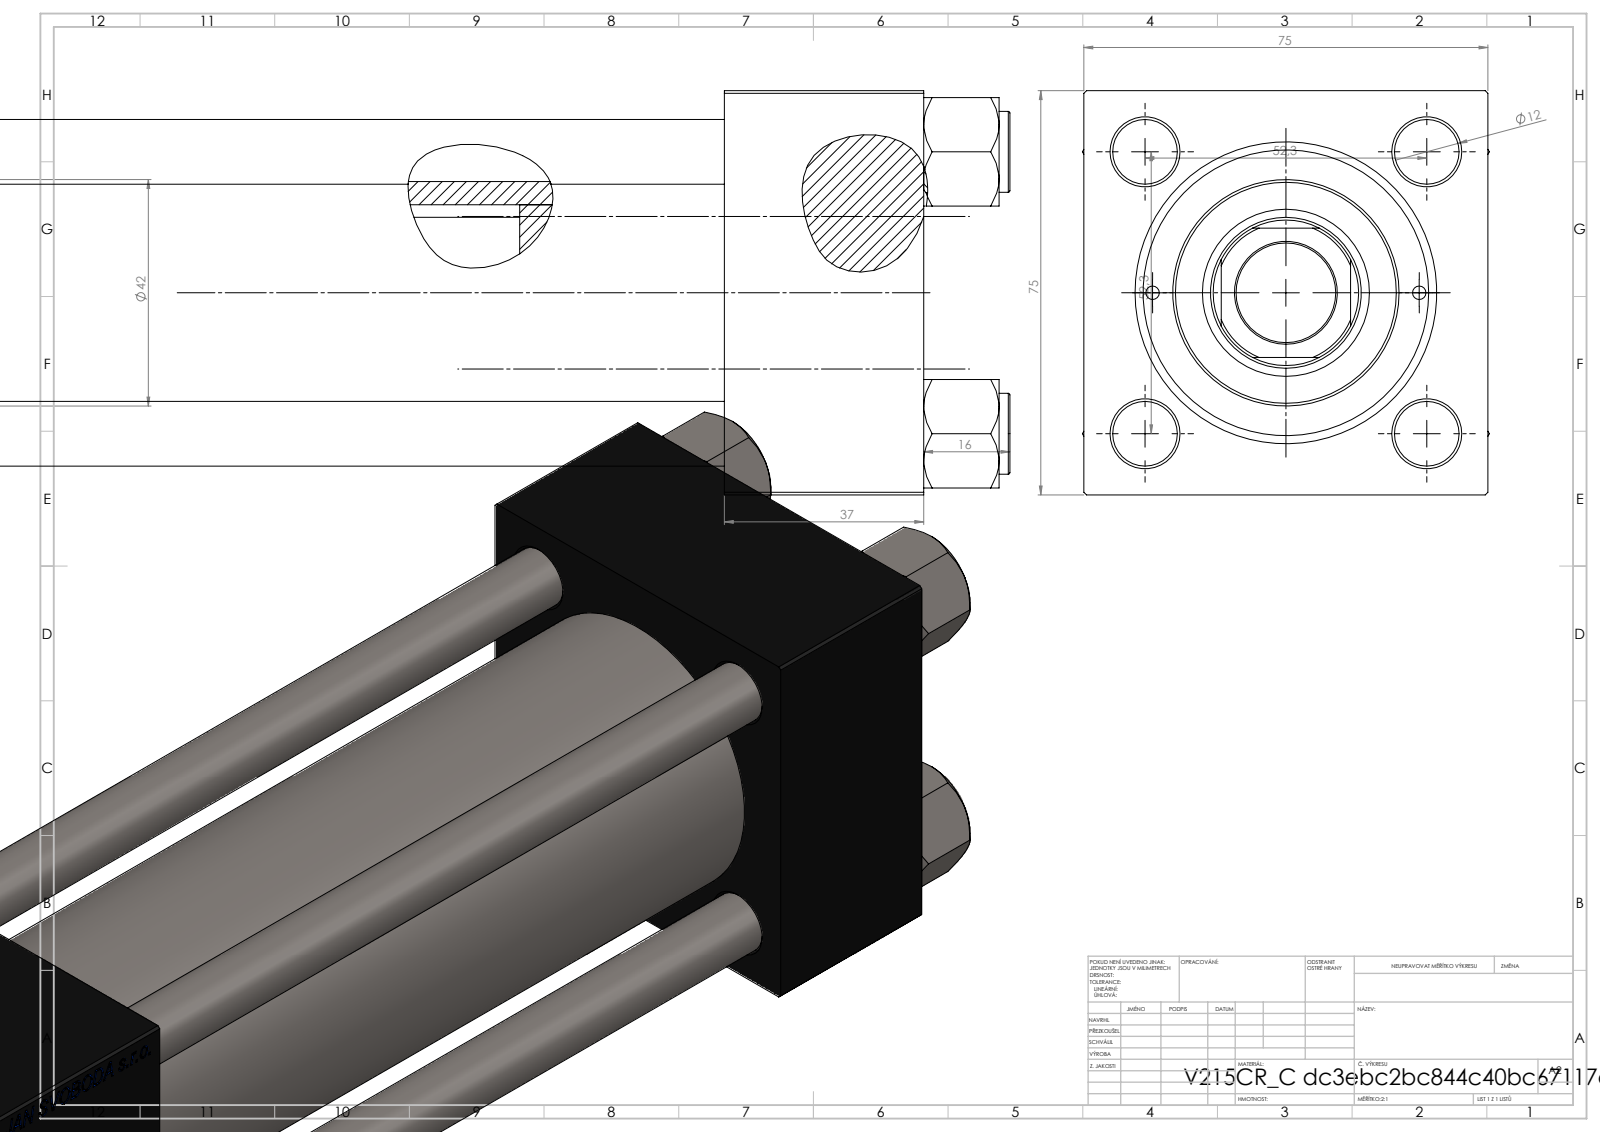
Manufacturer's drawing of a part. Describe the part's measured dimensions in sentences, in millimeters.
The part is named "V215_VC_A; NUT_M5_C; V215CR_C_Body; V215CR_VCP_C (+1 more)". Its 3-D file was written by "SolidWorks 2019 (CONFIG_CONTROL_DESIGN)". It is 11 solids with 1155 faces: 528 planar, 91 cylindrical and 536 other. Overall it measures 300 by 75.54 by 75 millimeters. Its volume is 833 549 cubic millimeters and its surface area 211 047 square millimeters. Round holes: 4 of diameter 12, 2 of diameter 2.5, 2 of diameter 7, 2 of diameter 20.96, 2 of diameter 30, 1 of diameter 18.5, 1 of diameter 28, 1 of diameter 31, 1 of diameter 41, 1 of diameter 50, 1 of diameter 53. Round bosses or shafts: 4 of diameter 15, 1 of diameter 56, 1 of diameter 42. Partial cylindrical surfaces (rounded edges, fillets, slot ends): 1 of radius 13.5. The main face-to-face distances are 75, 37, 259, 222, 200, 163, 59, 230.3, 193.3, 30.3. The hole center spacings are 26.19, 36.98, 52.3, 57.22, 24.75, 73.96, 49.5, 198.5.
